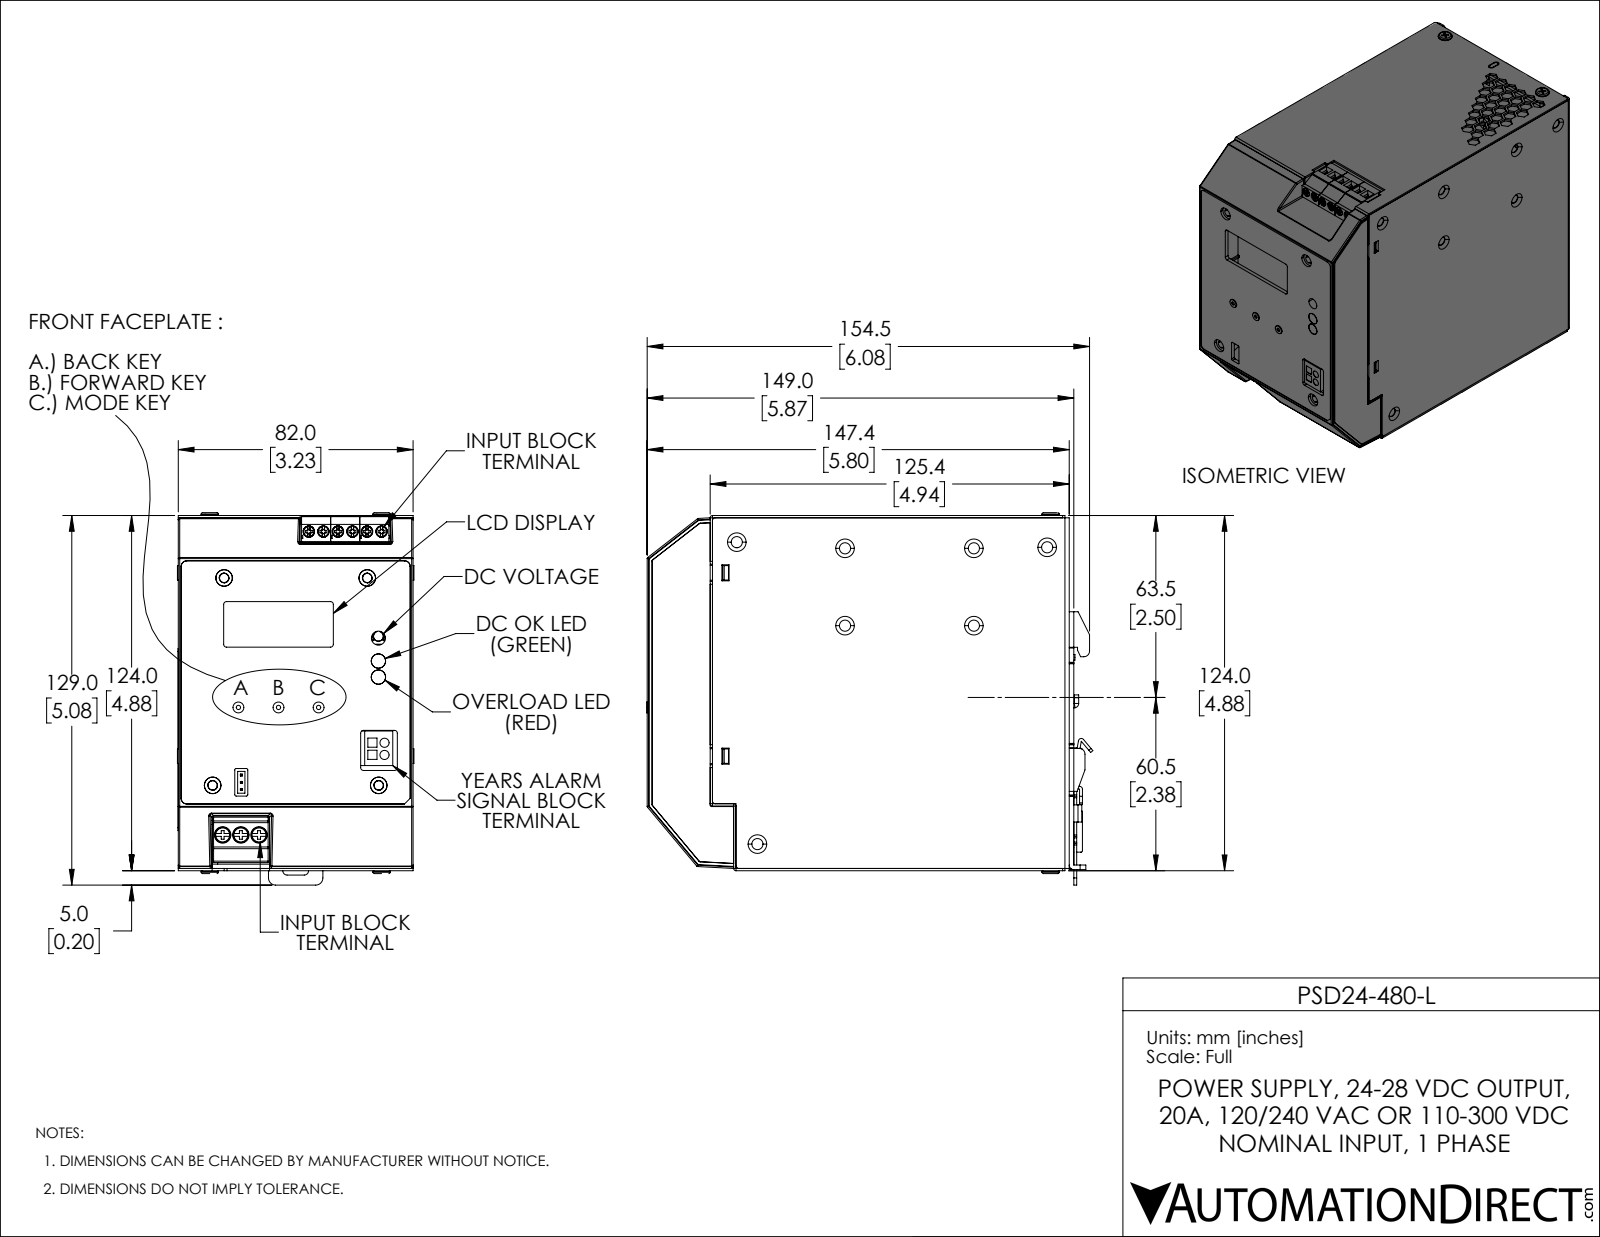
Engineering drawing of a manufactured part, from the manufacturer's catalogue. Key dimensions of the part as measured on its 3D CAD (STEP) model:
Part name (STEP PRODUCT): PSD24-480-L
STEP written by: SolidWorks 2019 (AUTOMOTIVE_DESIGN)
Units: inches
Bodies: 32 solids, 3358 faces (2481 planar, 565 cylindrical, 312 other)
Overall size (bounding box): 6.132 × 5.119 × 3.252
Volume: 8.366 in³ · Surface area: 322.4 in²
Round holes (diameter × count): ⌀0.154 ×14, ⌀0.157 ×8, ⌀0.098 ×6, ⌀0.138 ×6, ⌀0.142 ×4, ⌀0.193 ×3, ⌀0.039 ×2, ⌀0.118 ×2, ⌀0.126 ×2, ⌀0.031 ×1, ⌀0.146 ×1, ⌀0.165 ×1
Round bosses / shafts (diameter × count): ⌀0.217 ×6, ⌀0.154 ×6, ⌀0.226 ×3, ⌀0.236 ×2, ⌀0.156 ×2, ⌀0.134 ×2, ⌀0.114 ×2, ⌀0.079 ×2
Partial cylindrical surfaces — rounded edges, fillets, slot ends (radius × count): R0.02 ×87, R0.01 ×60, R0.039 ×58, R0.004 ×32, R0.012 ×32, R0.008 ×16, R0.079 ×10, R0.059 ×7
Main face-to-face distances: 0.059, 3.169, 0.031, 4.85, 3.228, 3.11, 4.819, 4.882, 4.937, 4.878
Hole centre spacings: 0.2, 0.4, 0.6, 0.787, 2.066, 0.466, 0.555, 0.742
